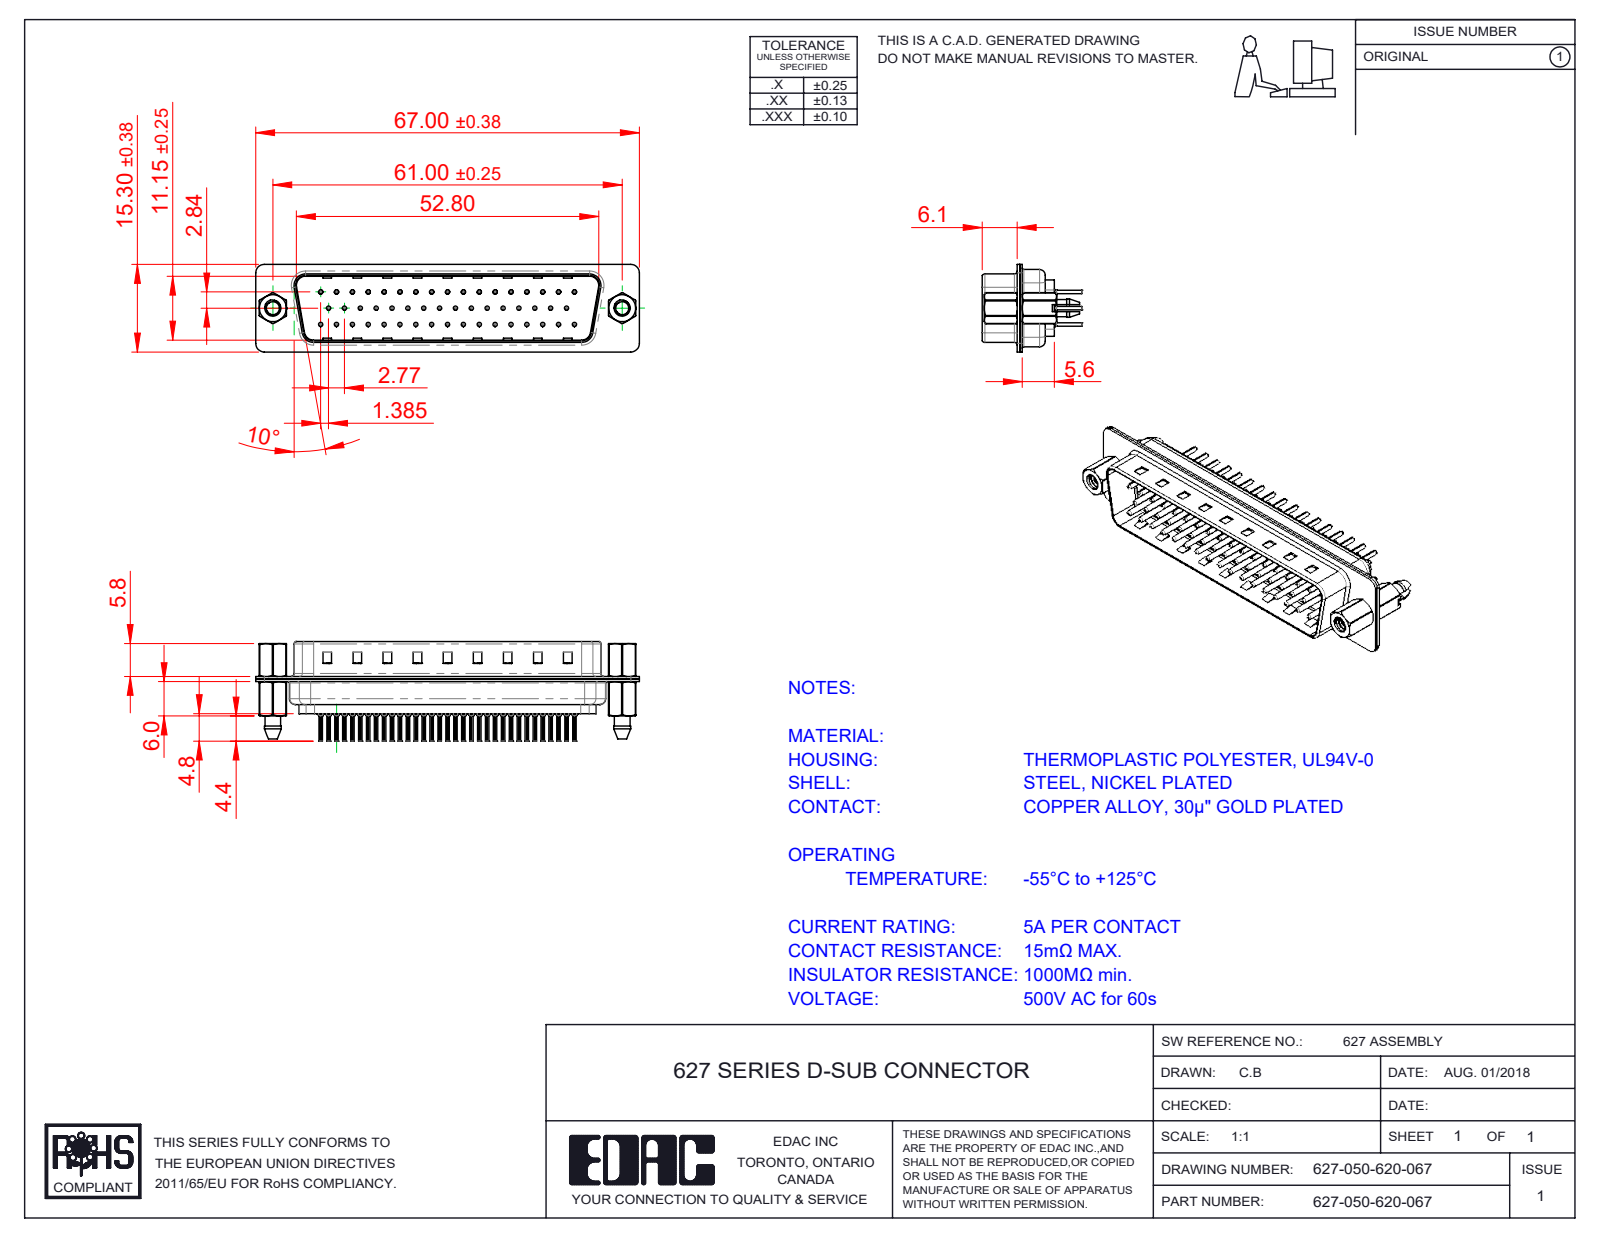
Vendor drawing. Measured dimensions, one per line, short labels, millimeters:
name: 627 4-40 Threaded Boardlock_LP; 627-050-620-067; 627 Shell Front_50 Contacts; 627 Contact Row 2_20L (+5 more)
written by: SolidWorks 2020 (CONFIG_CONTROL_DESIGN)
unit: mm
bodies: 57 solids, 5512 faces (1457 planar, 2095 cylindrical, 1960 other)
size: 67 × 17.3 × 15.3
volume: 4 751 mm³; area: 13 358 mm²
holes: 50× ⌀0.2, 50× ⌀0.35, 50× ⌀1.1, 50× ⌀1.6, 2× ⌀2.26, 2× ⌀2.29, 2× ⌀4, 2× ⌀4.8
bosses: 50× ⌀2, 50× ⌀1.5, 50× ⌀0.75, 50× ⌀0.6, 2× ⌀4.9, 2× ⌀2.79
rounds: 100× R0.1, 18× R1.5, 12× R2, 10× R1.6, 8× R0.5, 4× R0.25, 4× R0.6, 4× R0.65
face distances: 0.4, 0.45, 11.55, 0.9, 6.05, 6.5, 0.78, 12.33, 1.95, 0.77
hole spacings: 3.16, 2.77, 5.54, 8.31, 11.08, 13.85, 16.62, 5.03
